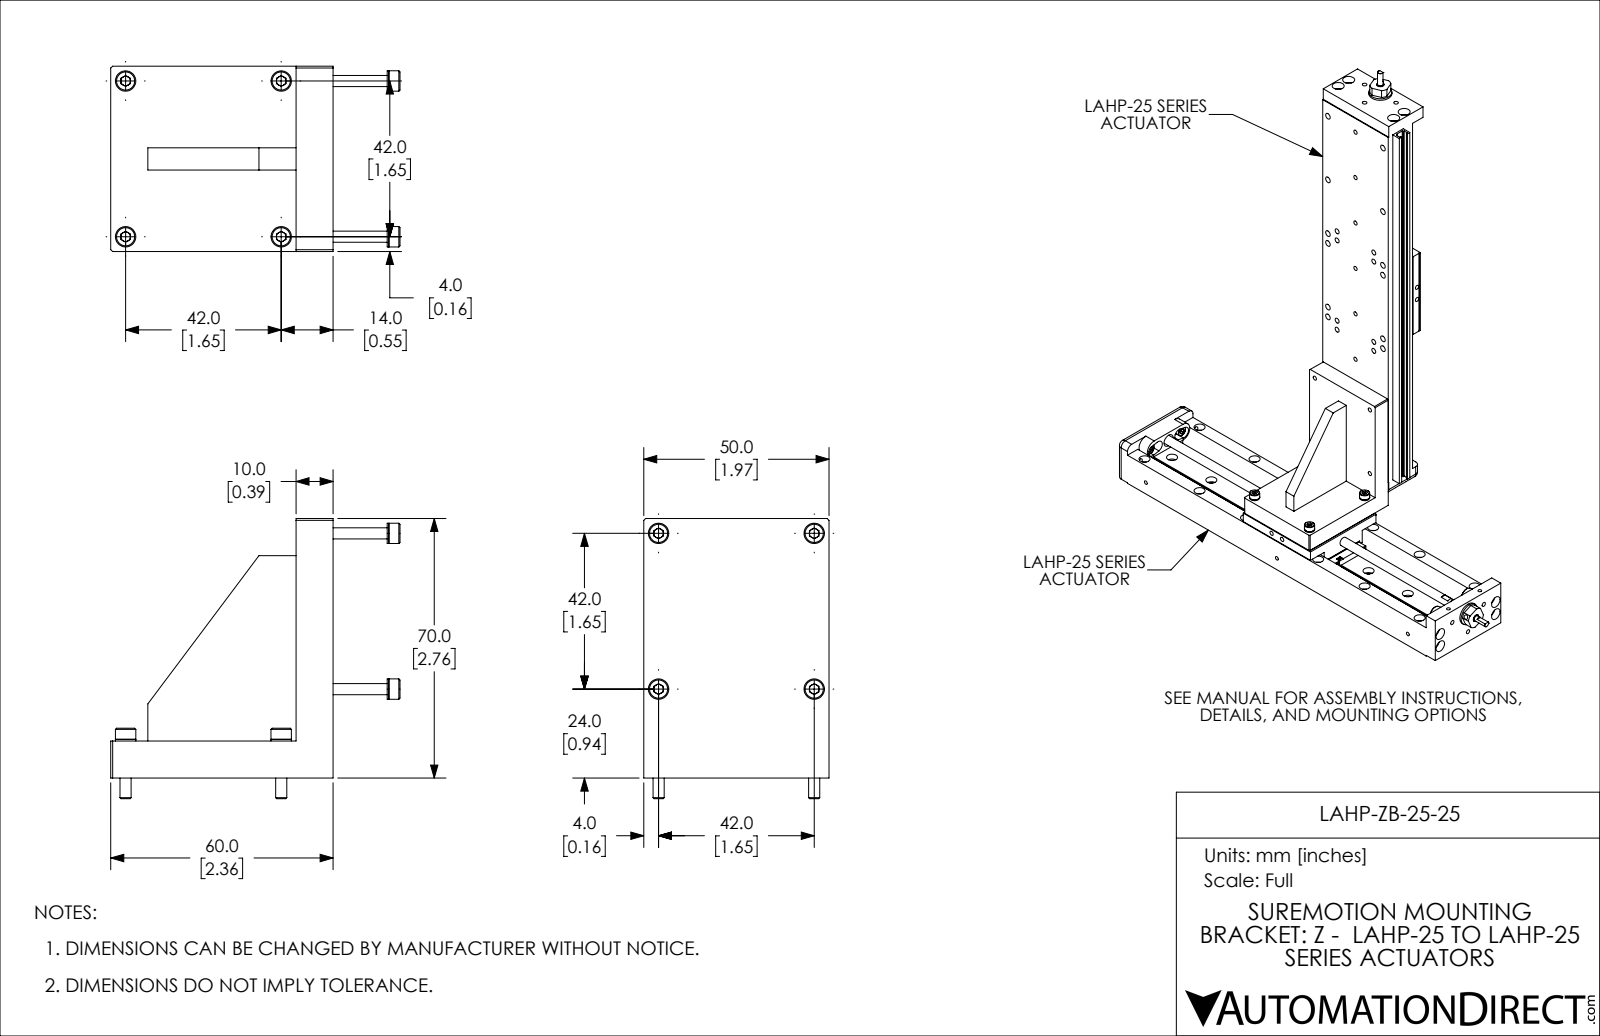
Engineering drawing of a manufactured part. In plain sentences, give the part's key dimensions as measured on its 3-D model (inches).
The part is named "LAHP-ZB-25-25". Its 3-D file was written by "SolidWorks 2019 (CONFIG_CONTROL_DESIGN)". It is 17 solids with 297 faces: 153 planar, 80 cylindrical and 64 other. Overall it measures 3.073 by 2.974 by 1.969 inches. Its volume is 4.234 cubic inches and its surface area 32.96 square inches. Round holes: 8 of diameter 0.126, 4 of diameter 0.098, 4 of diameter 0.138. Round bosses or shafts: 8 of diameter 0.217, 8 of diameter 0.118. The main face-to-face distances are 0.394, 0.866, 1.102, 1.969, 0.236, 2.362, 2.756, 0.018, 0.593, 0.986. The hole center spacings are 1.654, 2.339.
